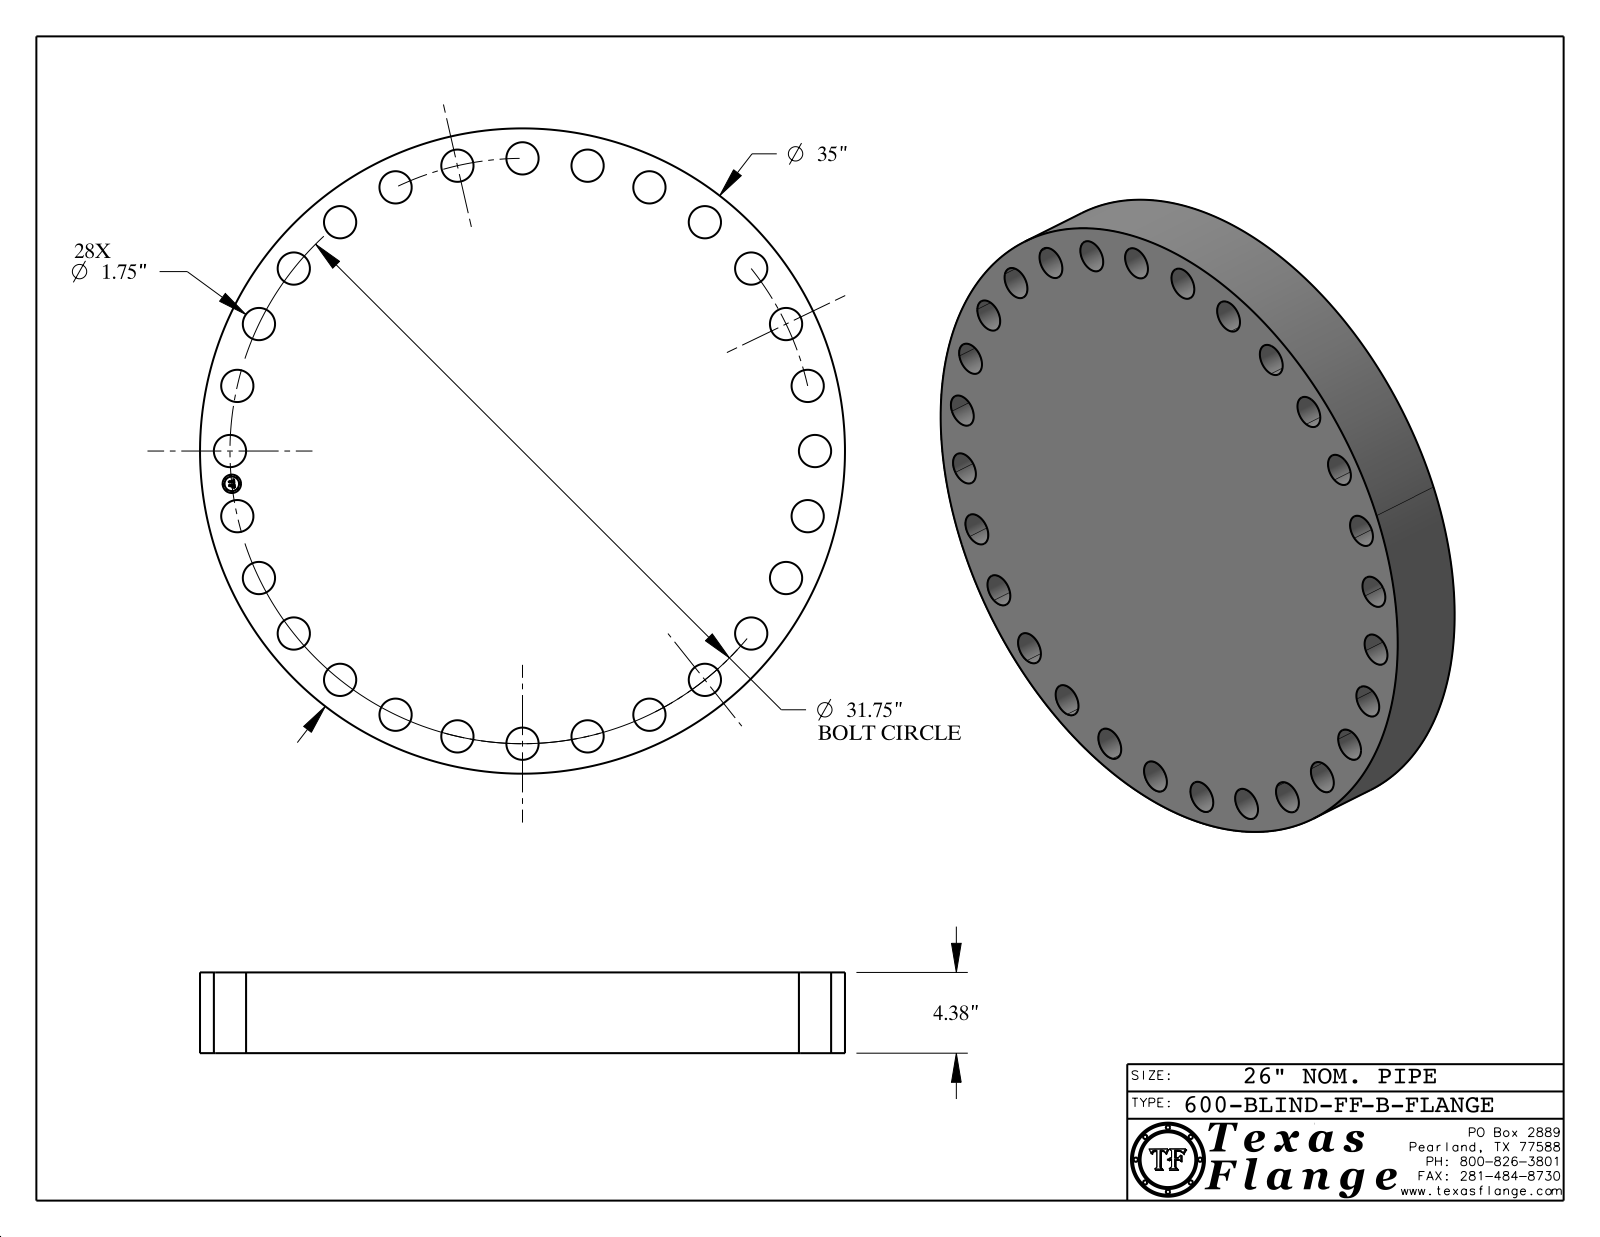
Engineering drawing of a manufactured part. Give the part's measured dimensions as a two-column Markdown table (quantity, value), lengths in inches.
| quantity | value |
| --- | --- |
| part name | 600-BLIND-FF, Series B |
| STEP written by | CATIA V5 STEP AP214 (AUTOMOTIVE_DESIGN) |
| units | inches |
| bodies | 1 solid, 445 faces (367 planar, 78 cylindrical, 0 other) |
| overall size | 35 × 35 × 4.38 |
| volume | 3 919 in³ |
| surface area | 2 946 in² |
| round holes (diameter × count) | 1.75 × 28, 1 × 1 |
| round bosses / shafts (diameter × count) | 0.061 × 8, 35 × 1, 0.788 × 1 |
| main face-to-face distances | 4.38, 0.015, 4.365, 0.298, 0.293, 0.054, 0.193, 0.248, 0.013, 0.044 |
| hole center spacings | 16.892, 28.606, 29.969, 30.954, 13.776, 19.796, 3.555, 7.065 |
